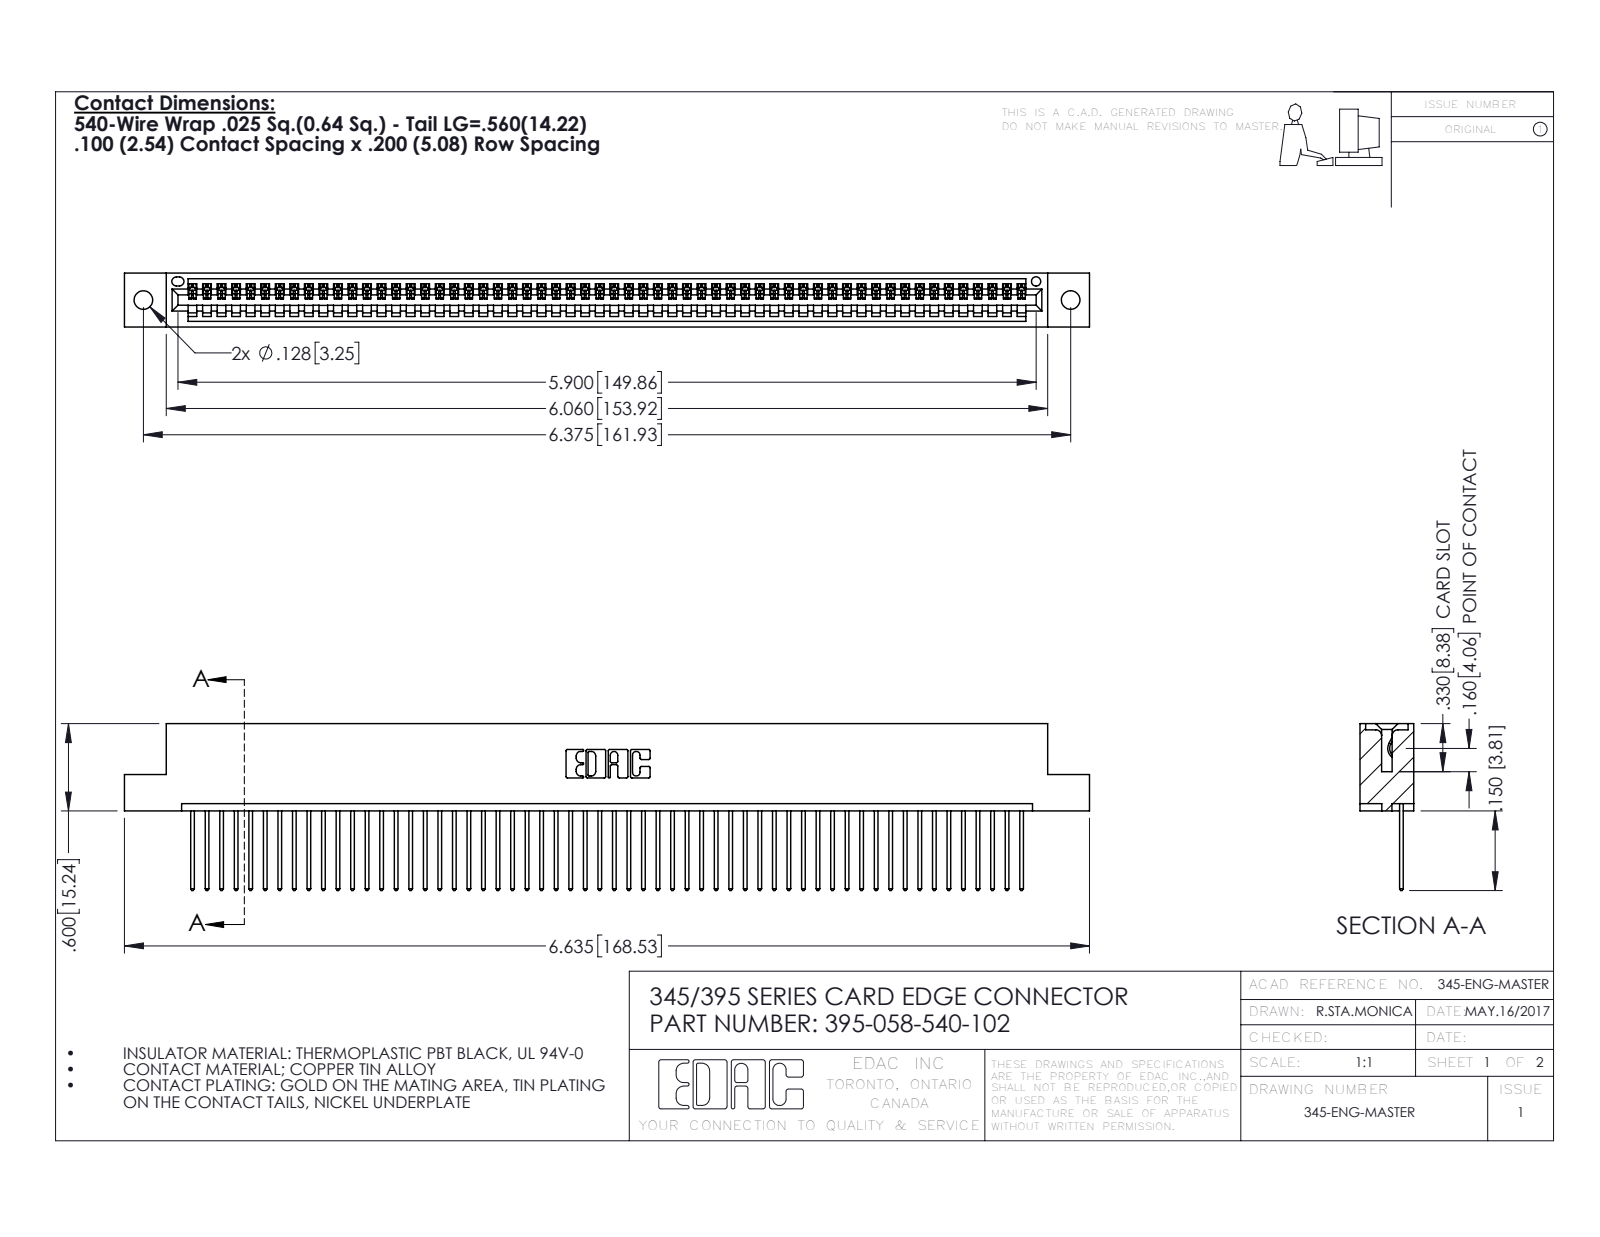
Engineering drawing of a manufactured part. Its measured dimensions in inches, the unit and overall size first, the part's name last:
Units: inches
Overall size (bounding box): 6.635 × 1.147 × 0.37
Round holes (diameter × count): ⌀0.128 ×2, ⌀0.064 ×1
Partial cylindrical surfaces — rounded edges, fillets, slot ends (radius × count): R0.006 ×116, R0.01 ×116, R0.01 ×22, R0.007 ×6, R0.031 ×6, R0.026 ×3, R0.031 ×2, R0.04 ×2
Main face-to-face distances: 0.298, 0.072, 0.37, 0.098, 0.272, 0.025, 0.2, 0.225, 0.149, 0.072
Hole centre spacings: 0.27, 6.139, 6.375
Volume: 0.987 in³ · Surface area: 34.12 in²
Bodies: 59 solids, 3490 faces (2400 planar, 1090 cylindrical, 0 other)
Part name (STEP PRODUCT): 345-292-001_345-293-140; 395-058-540-102; 345 Part_Flush Mounting Lugs - 0.128 Dia
STEP written by: SolidWorks 2016 (CONFIG_CONTROL_DESIGN)
